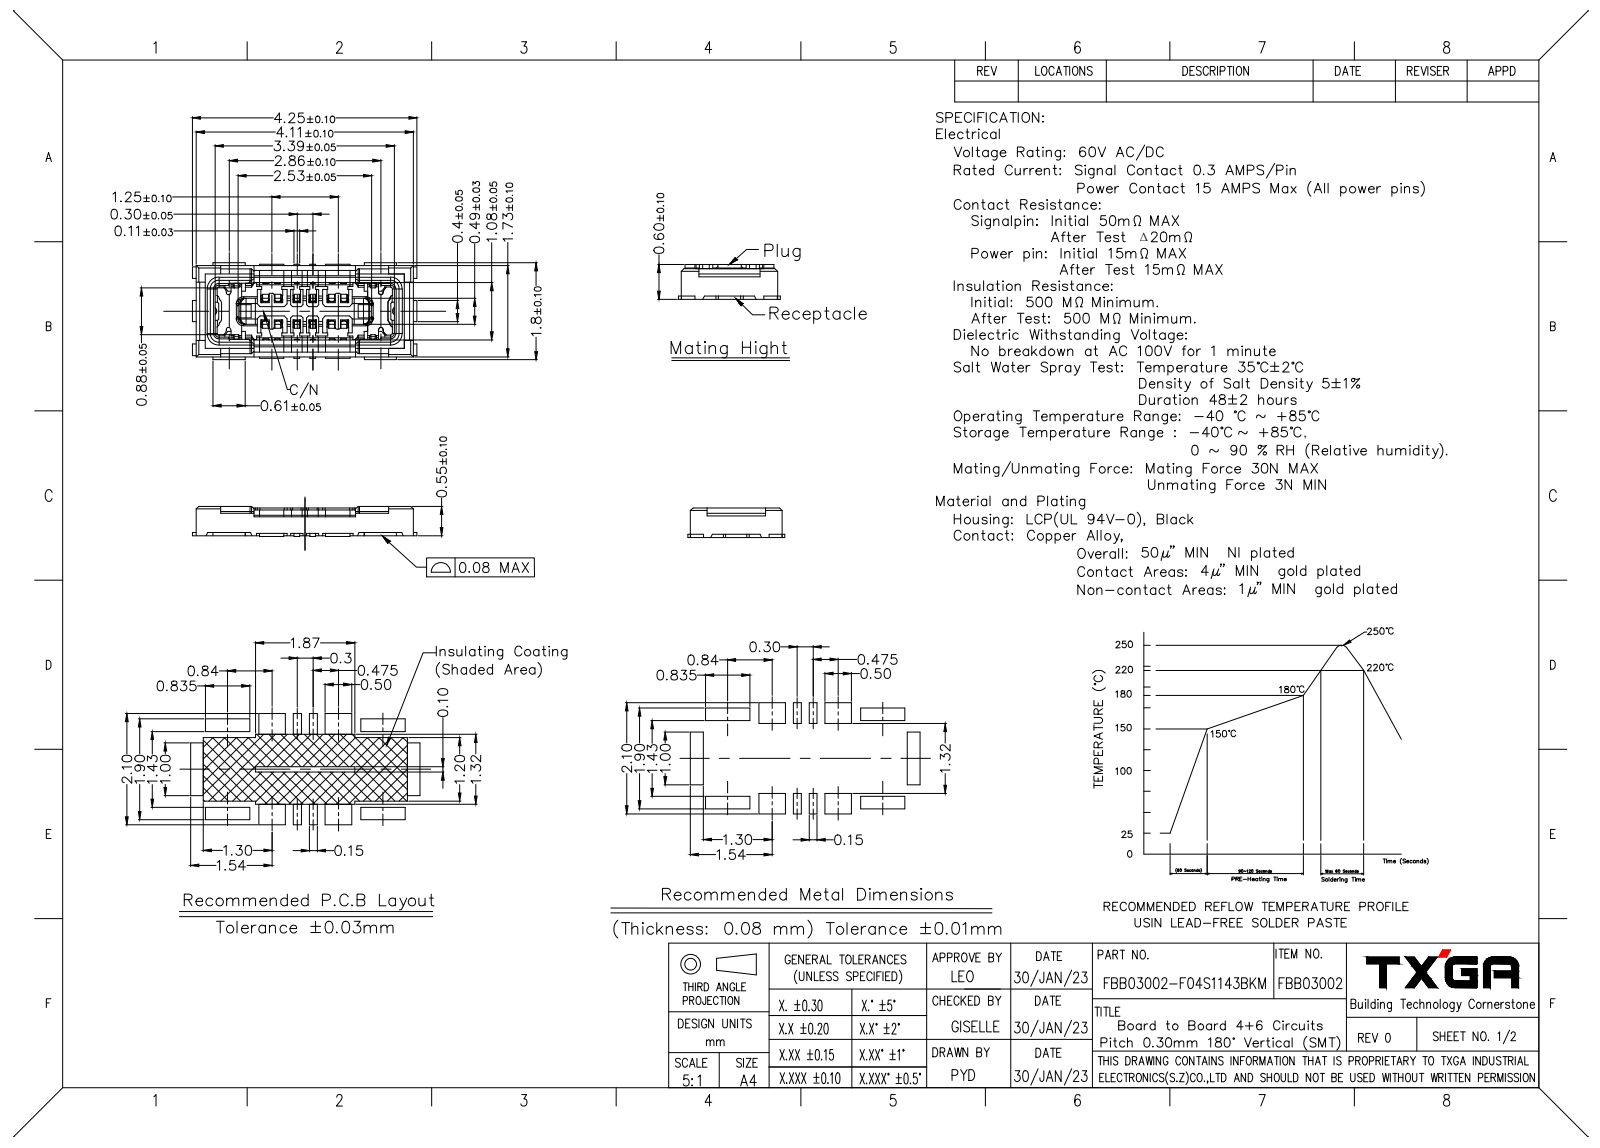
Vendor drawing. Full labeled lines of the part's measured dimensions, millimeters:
Part name (STEP PRODUCT): R
STEP written by: CREO PARAMETRIC BY PTC INC, 2019010 (AUTOMOTIVE_DESIGN)
Units: millimetres
Bodies: 1 solid, 747 faces (456 planar, 182 cylindrical, 109 other)
Overall size (bounding box): 4.33 × 2.1 × 0.55
Volume: 3 mm³ · Surface area: 28 mm²
Partial cylindrical surfaces — rounded edges, fillets, slot ends (radius × count): R0.1 ×22
Main face-to-face distances: 1.72, 0.32, 0.62, 1.1, 0.78, 0.42, 1.4, 0.37, 0.46, 0.48
